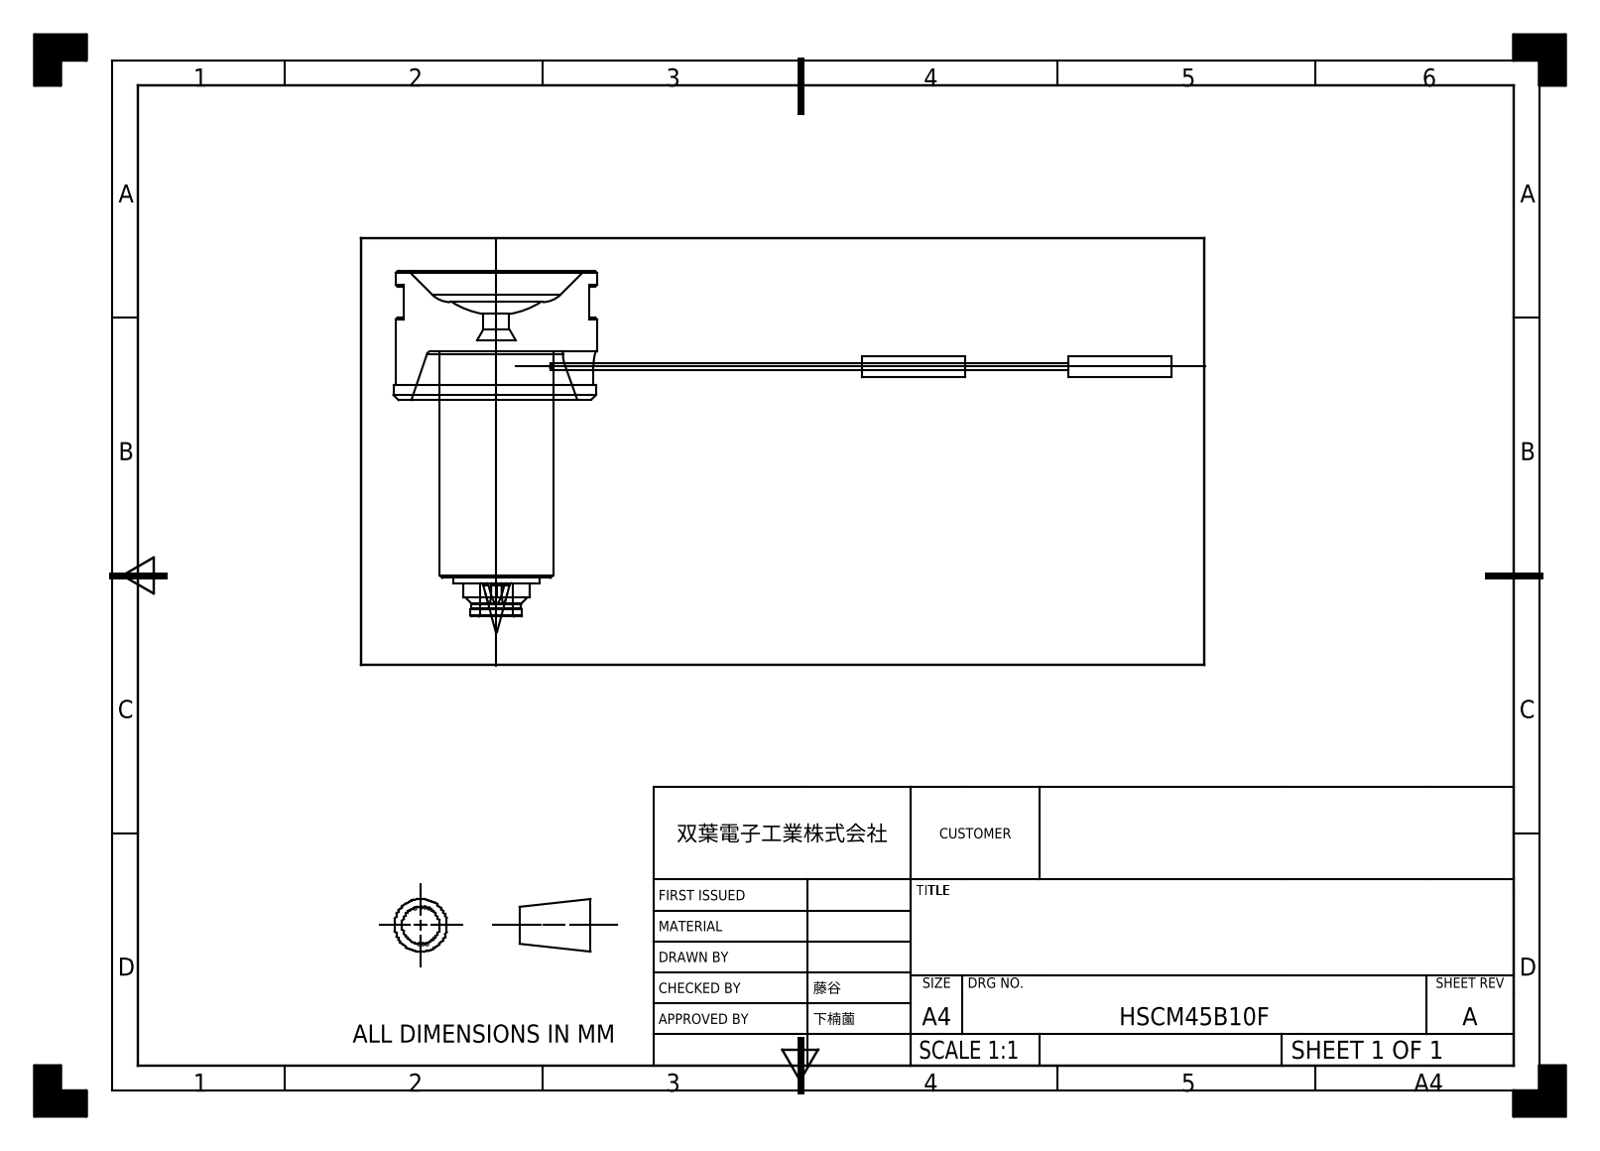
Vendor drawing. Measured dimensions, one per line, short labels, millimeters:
name: HSCM45B10F
written by: SIEMENS PLM Software NX 2023 (AUTOMOTIVE_DESIGN)
unit: mm
bodies: 1 solid, 75 faces (30 planar, 23 cylindrical, 22 other)
size: 151 × 70 × 40
volume: 36 793 mm³; area: 11 067 mm²
holes: 1× ⌀5, 1× ⌀6.35
bosses: 2× ⌀4, 2× ⌀1.2, 1× ⌀40, 1× ⌀39, 1× ⌀22, 1× ⌀16.9, 1× ⌀10, 1× ⌀9.6
rounds: 3× R2.8, 2× R3, 1× R7.45
face distances: 25, 9.5, 15.5, 45, 59.5, 44, 34.5, 3, 6.5, 60.5
